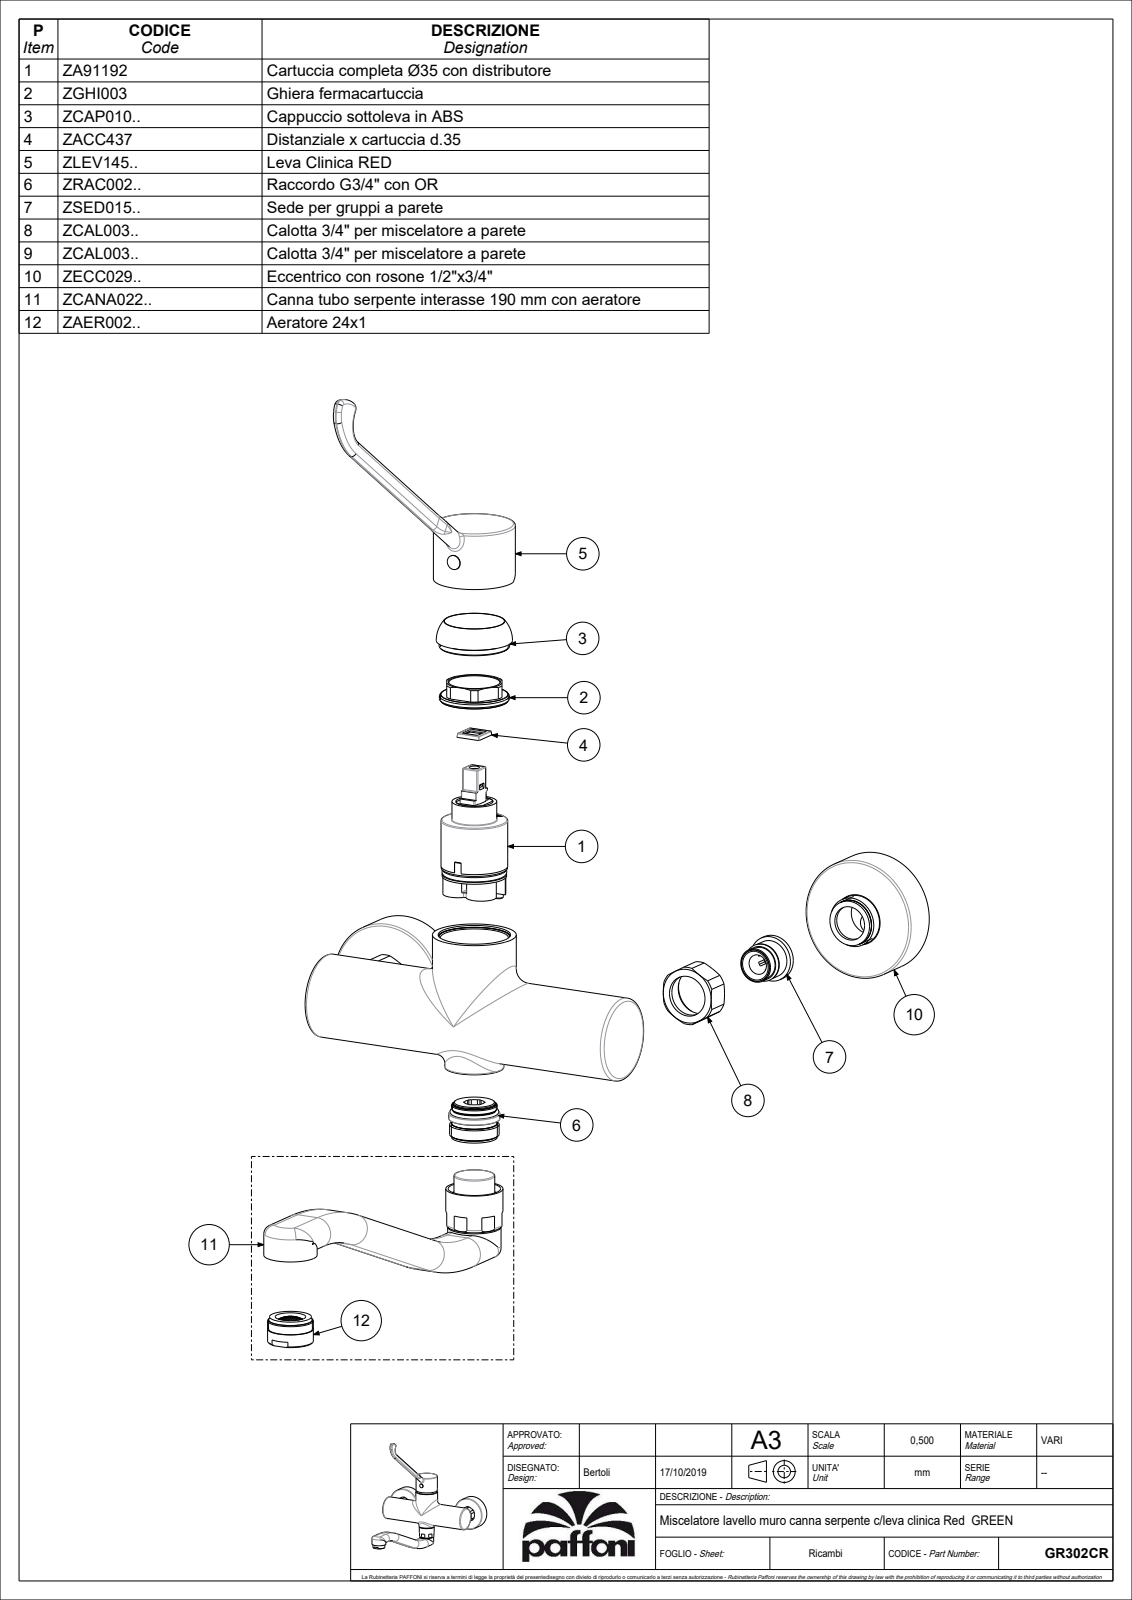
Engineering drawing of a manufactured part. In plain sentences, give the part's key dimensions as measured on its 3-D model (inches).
The part is named "GR302CR". Its 3-D file was written by "CREO PARAMETRIC BY PTC INC, 2020044 (CONFIG_CONTROL_DESIGN)". It is 5 solids with 2847 faces: 2008 planar, 472 cylindrical and 367 other. Overall it measures 10.413 by 9.606 by 8.406 inches. Its volume is 13.51 cubic inches and its surface area 273.7 square inches. Round holes: 3 of diameter 0.354, 3 of diameter 0.472, 3 of diameter 0.984, 2 of diameter 0.276, 2 of diameter 0.315, 2 of diameter 0.413, 2 of diameter 0.63, 2 of diameter 0.709, 2 of diameter 0.807, 2 of diameter 0.846, 2 of diameter 0.949, 2 of diameter 1.051. Round bosses or shafts: 3 of diameter 0.945, 2 of diameter 2.5, 2 of diameter 1.732, 2 of diameter 1.102, 2 of diameter 1.063, 2 of diameter 0.776, 2 of diameter 0.354, 1 of diameter 1.693. Partial cylindrical surfaces (rounded edges, fillets, slot ends): 105 of radius 0.02, 20 of radius 0.012, 14 of radius 0.008, 6 of radius 0.039, 6 of radius 0.283, 6 of radius 0.315, 4 of radius 0.079, 3 of radius 0.285. The main face-to-face distances are 0.024, 0.63, 0.031, 4.429, 0.807, 0.598, 0.177, 2.697, 0.778, 3.346. The hole center spacings are 0.028, 0.335, 0.339, 0.513, 0.52, 0.532, 3.841, 7.386.
